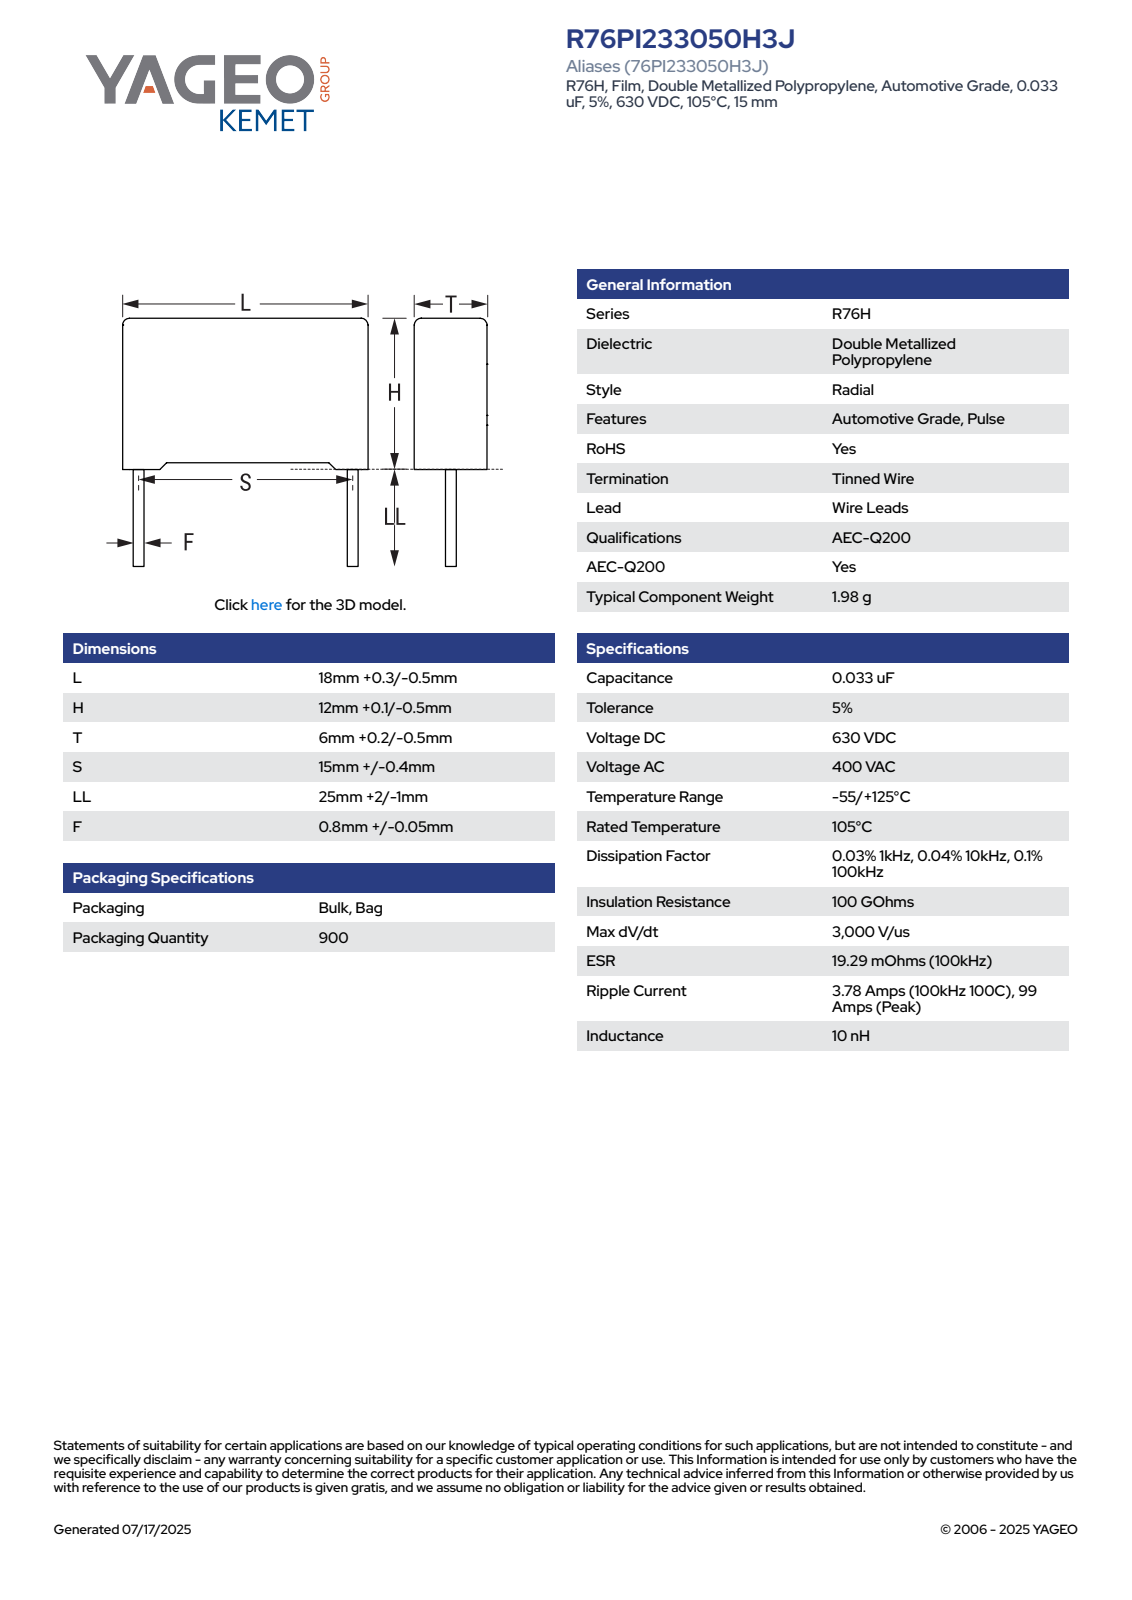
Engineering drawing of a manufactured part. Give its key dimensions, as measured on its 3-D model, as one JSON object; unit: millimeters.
{"part_name": "CFR_RB2R76_18X12X6_L18.3H12.1T6.2S15LL27F0.85", "step_written_by": "SolidWorks 2014 (AUTOMOTIVE_DESIGN)", "units": "millimeters", "bodies": {"solids": 4, "faces": 85, "planar": 77, "cylindrical": 8, "other": 0}, "overall_size": [39.1, 18.3, 6.21], "volume_mm3": 1332, "surface_area_mm2": 997, "round_bosses_or_shafts": [[0.85, 2]], "partial_cylinders_radius": [[0.5, 4]], "face_to_face_distances": [6.2, 11.35, 18.3, 0.61, 5.59, 0.75, 12.1, 0.42, 0.33, 11.68]}
